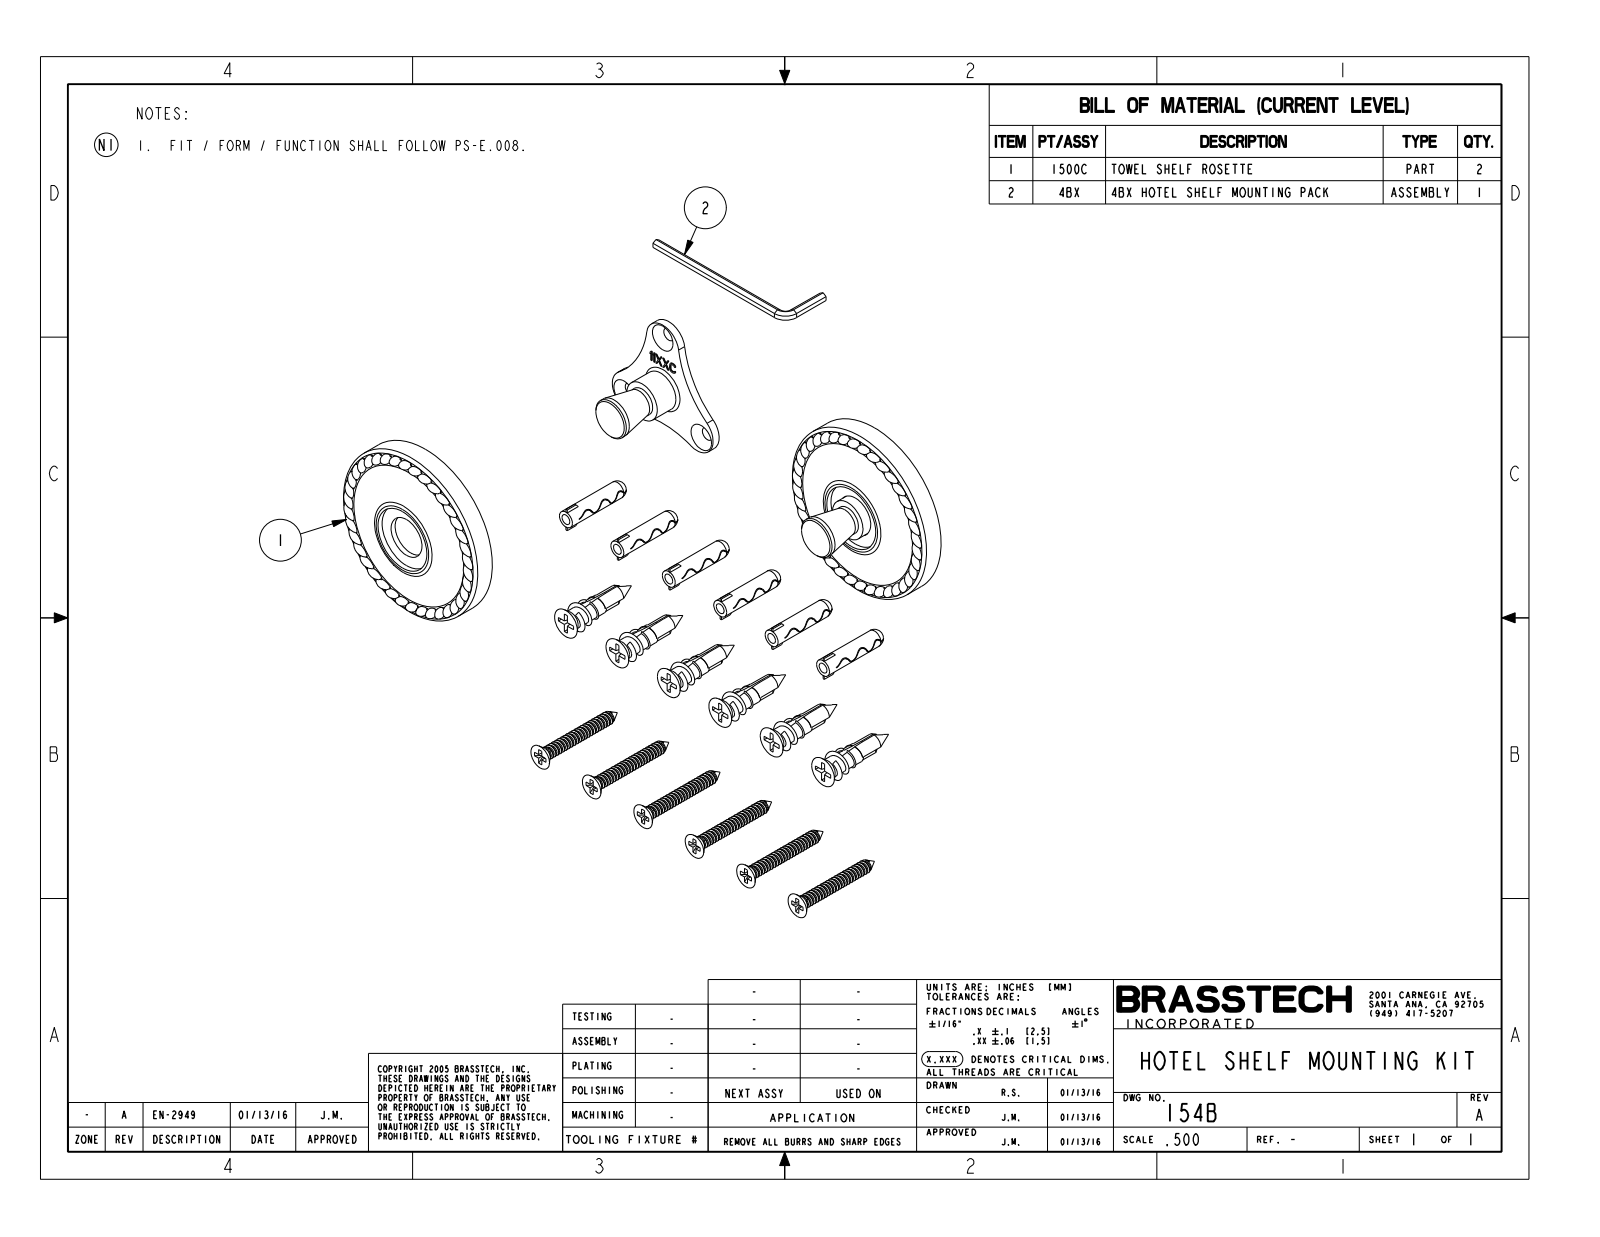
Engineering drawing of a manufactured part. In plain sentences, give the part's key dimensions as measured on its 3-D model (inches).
The part is named "1500C". Its 3-D file was written by "PRO/ENGINEER BY PARAMETRIC TECHNOLOGY CORPORATION, 2013150 (CONFIG_CONTROL_DESIGN)". It is 1 solid with 194 faces: 12 planar, 12 cylindrical and 170 other. Overall it measures 2.59 by 2.59 by 0.452 inches. Its volume is 0.626 cubic inches and its surface area 24.6 square inches. Round holes: 1 of diameter 0.6, 1 of diameter 0.948, 1 of diameter 2.432. Round bosses or shafts: 1 of diameter 2.59. The main face-to-face distances are 0.124, 0.373, 0.079, 0.294, 0.079, 0.249, 0.045, 0.328, 0.034, 0.045.
